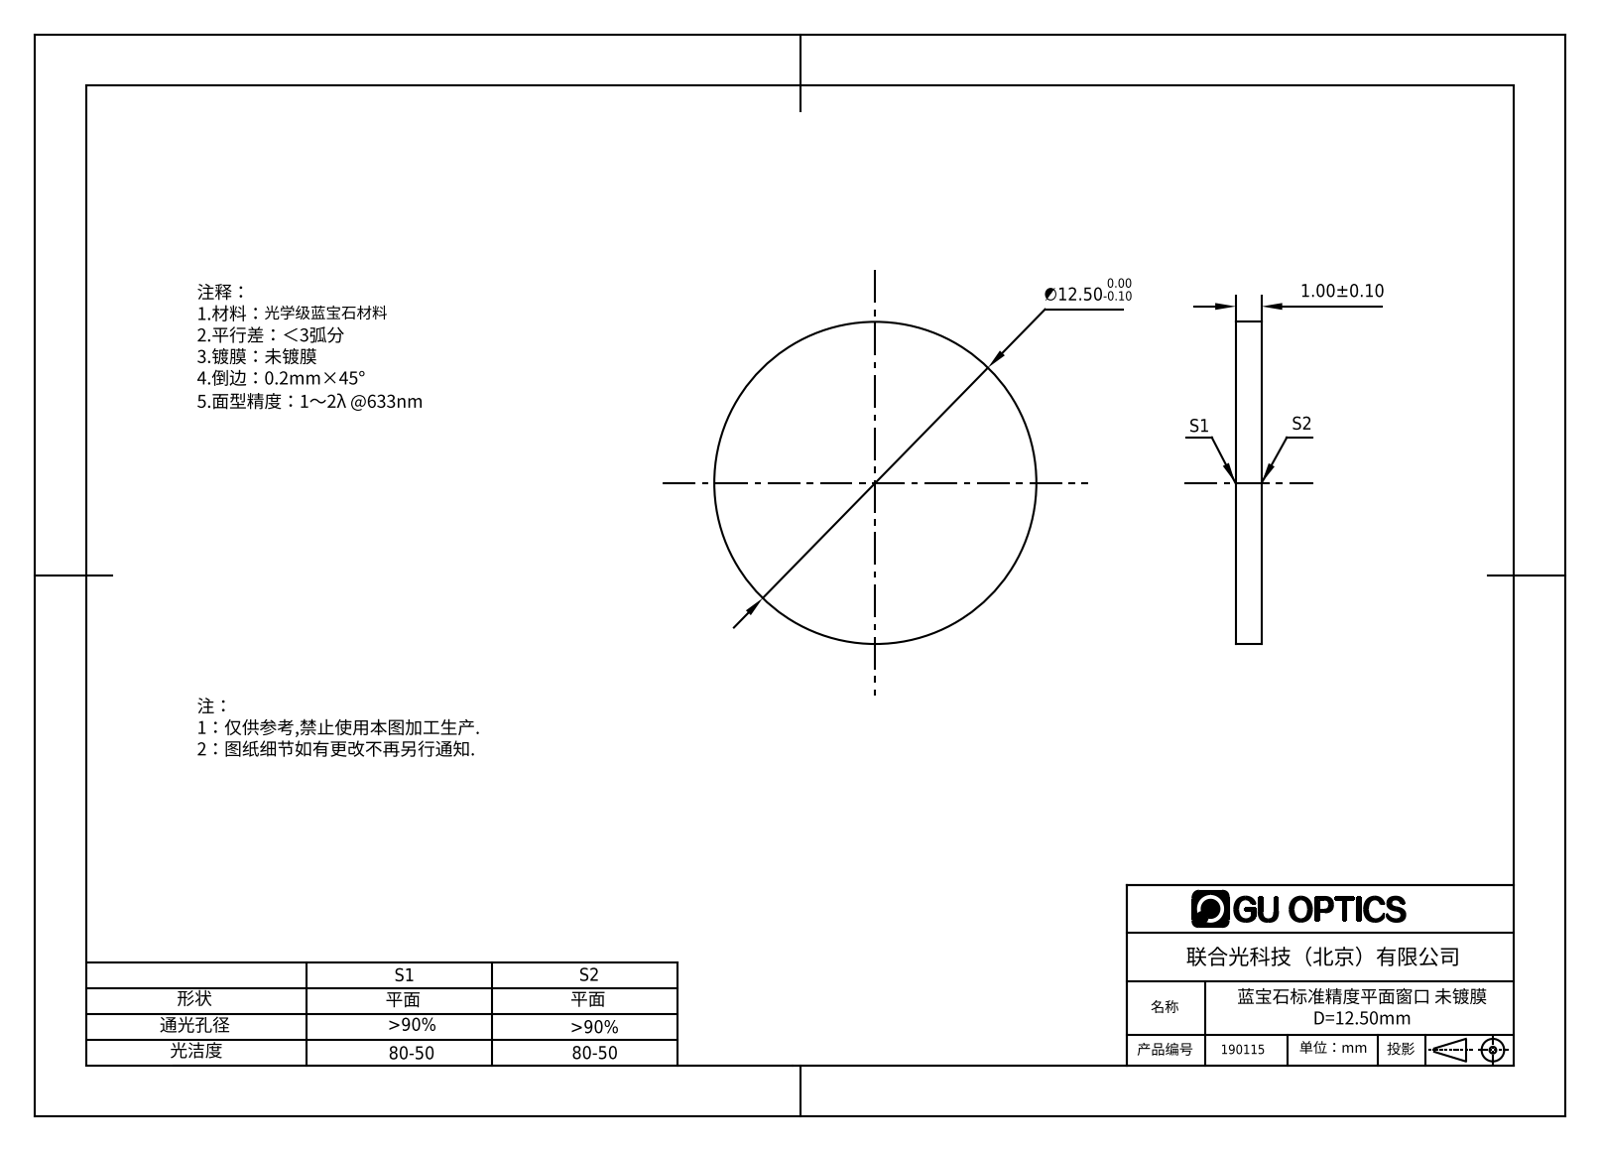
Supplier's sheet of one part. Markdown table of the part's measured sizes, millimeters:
| quantity | value |
| --- | --- |
| part name | 190115 |
| STEP written by | SolidWorks 2016 (AUTOMOTIVE_DESIGN) |
| units | millimeters |
| bodies | 1 solid, 4 faces (2 planar, 2 cylindrical, 0 other) |
| overall size | 12.5 × 12.5 × 1 |
| volume | 123 mm³ |
| surface area | 285 mm² |
| round bosses / shafts (diameter × count) | 12.5 × 1 |
| main face-to-face distances | 1 |
